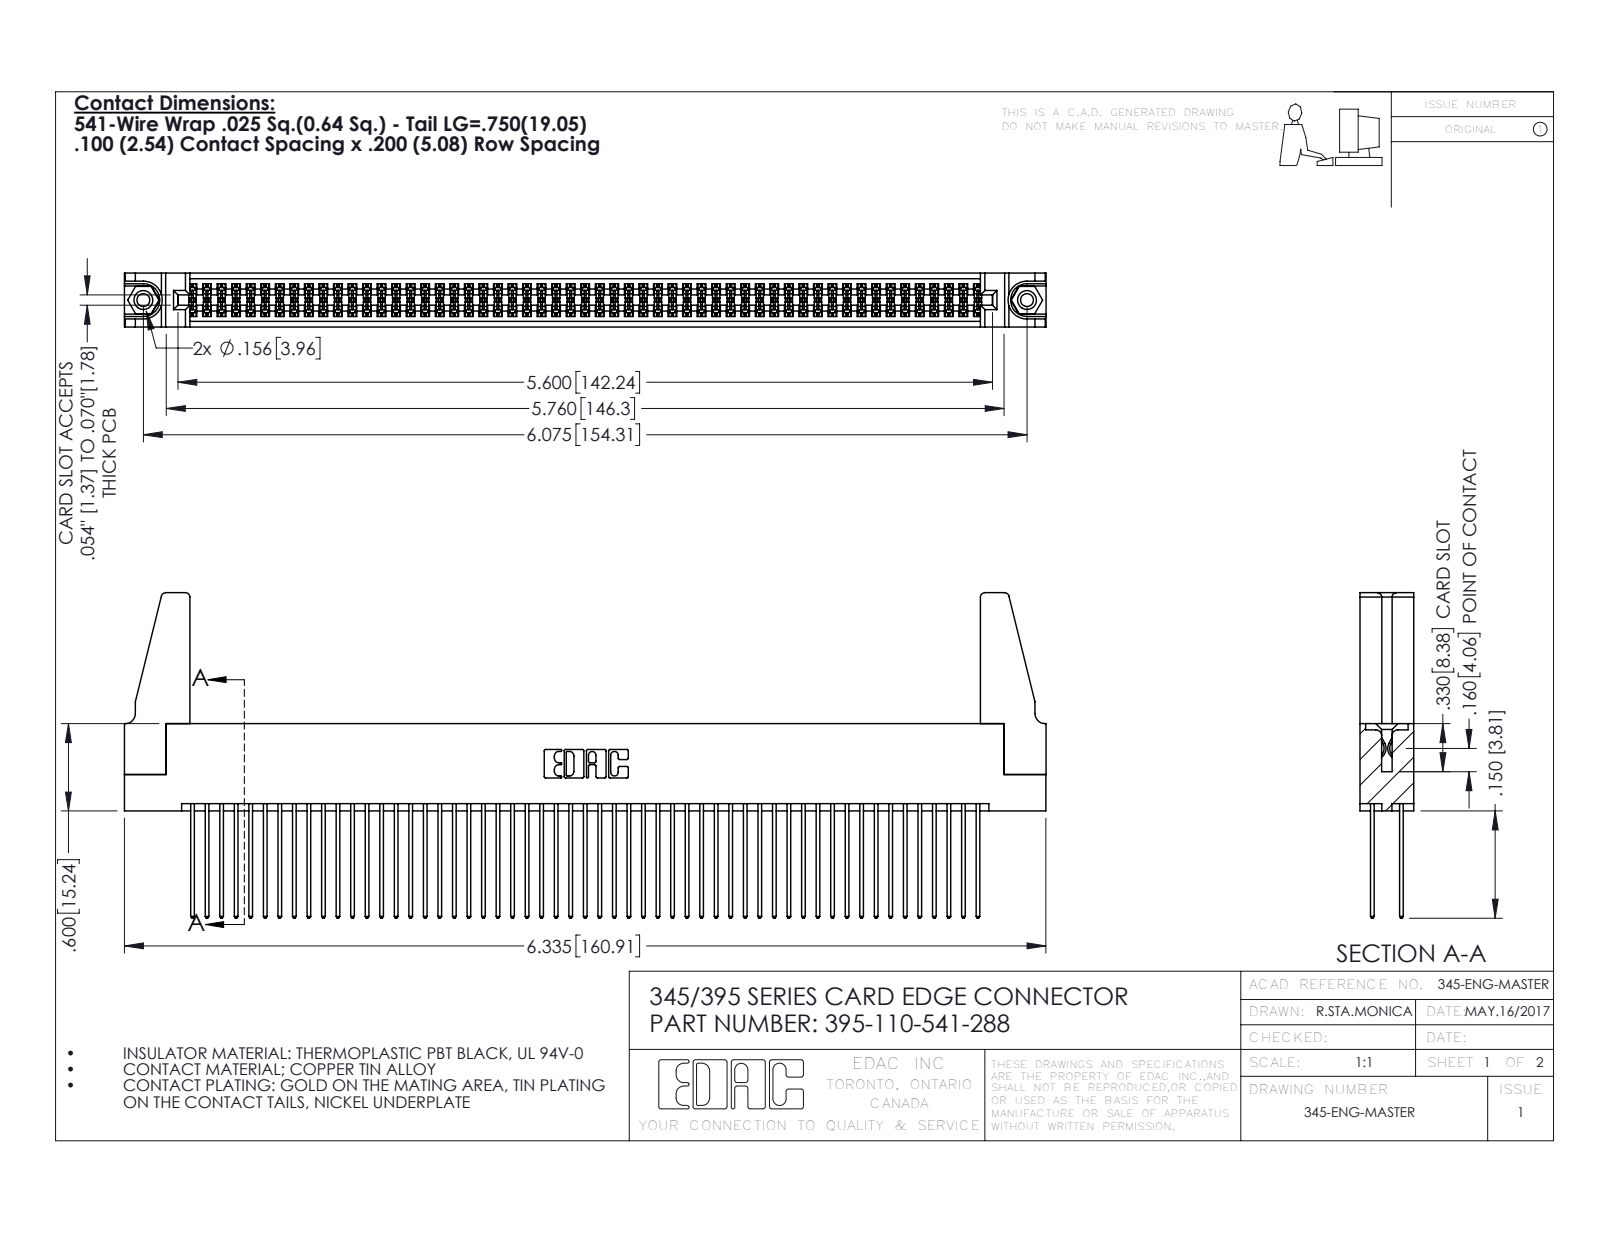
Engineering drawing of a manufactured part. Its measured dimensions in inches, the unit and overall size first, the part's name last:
Units: inches
Overall size (bounding box): 6.336 × 2.237 × 0.37
Round holes (diameter × count): ⌀0.089 ×2, ⌀0.125 ×2, ⌀0.156 ×2, ⌀0.064 ×1
Round bosses / shafts (diameter × count): ⌀0.155 ×2
Partial cylindrical surfaces — rounded edges, fillets, slot ends (radius × count): R0.006 ×165, R0.01 ×110, R0.01 ×22, R0.03 ×8, R0.007 ×6, R0.031 ×6, R0.026 ×3, R0.014 ×2
Main face-to-face distances: 0.072, 0.298, 0.2, 0.098, 0.272, 0.025, 0.37, 0.225, 0.175, 0.149
Hole centre spacings: 0.27, 5.839, 6.075
Volume: 1.198 in³ · Surface area: 47.37 in²
Bodies: 115 solids, 5750 faces (3782 planar, 1952 cylindrical, 16 other)
Part name (STEP PRODUCT): 345-250-001_345-250-001-102; 395-110-541-288; 345-220-078_345-220-088; 345-292-001_345-293-141 (+1 more)
STEP written by: SolidWorks 2016 (CONFIG_CONTROL_DESIGN)
